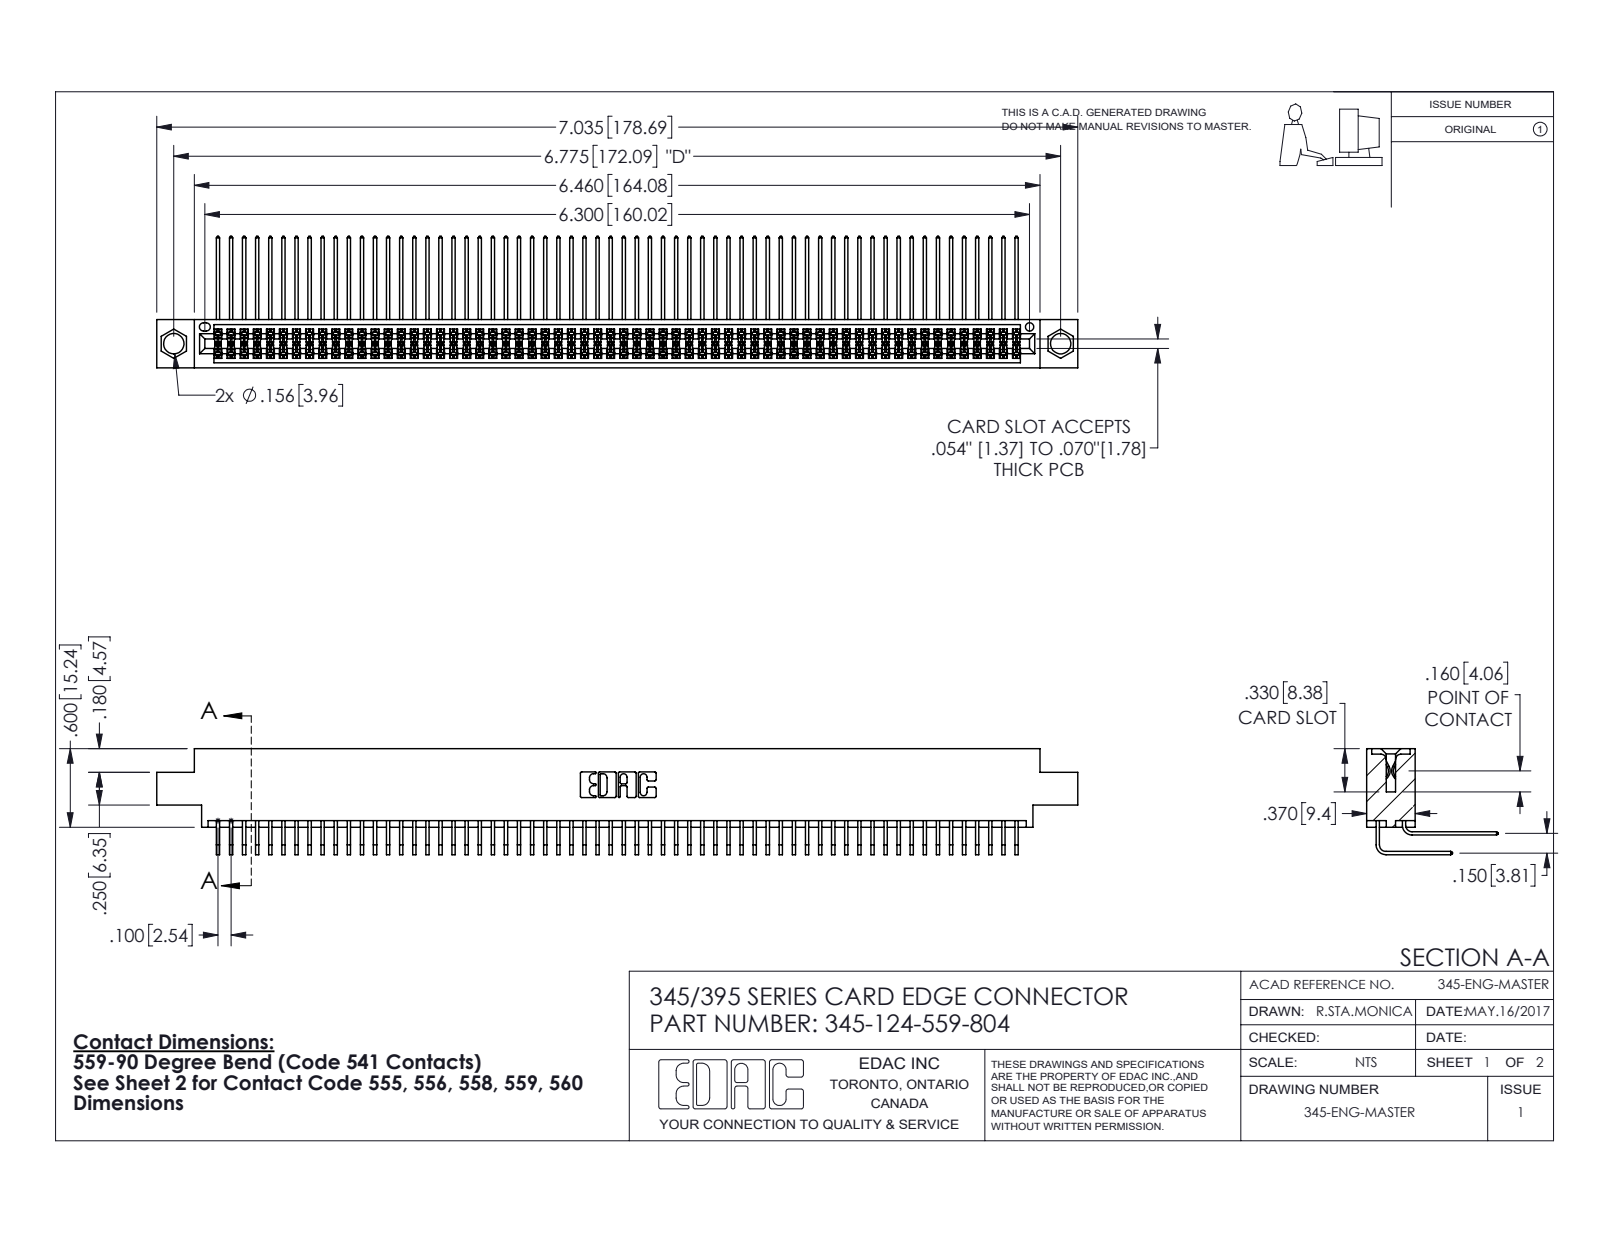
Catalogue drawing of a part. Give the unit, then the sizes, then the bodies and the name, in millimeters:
Units: millimetres
Overall size (bounding box): 178.7 × 25.5 × 20.5
Round holes (diameter × count): ⌀4 ×2, ⌀1.6 ×1
Partial cylindrical surfaces — rounded edges, fillets, slot ends (radius × count): R0.2 ×186, R0.3 ×22, R0.2 ×6, R0.8 ×6, R0.7 ×3, R0.4 ×2, R0.5 ×2, R0.6 ×2
Main face-to-face distances: 1.8, 7.6, 9.4, 5.1, 2.5, 6.9, 0.6, 5.7, 4.4, 3.8
Hole centre spacings: 6.9, 166.1, 172.1
Volume: 18 040 mm³ · Surface area: 30 410 mm²
Bodies: 125 solids, 6592 faces (4438 planar, 2154 cylindrical, 0 other)
Part name (STEP PRODUCT): 345-292-001_559 Tail - 2; 345-292-001_558 559 Tail - 1; 345 Part_0.170 Offset - 0.156 Dia-TI; 345-124-559-804
STEP written by: SolidWorks 2020 (CONFIG_CONTROL_DESIGN)
